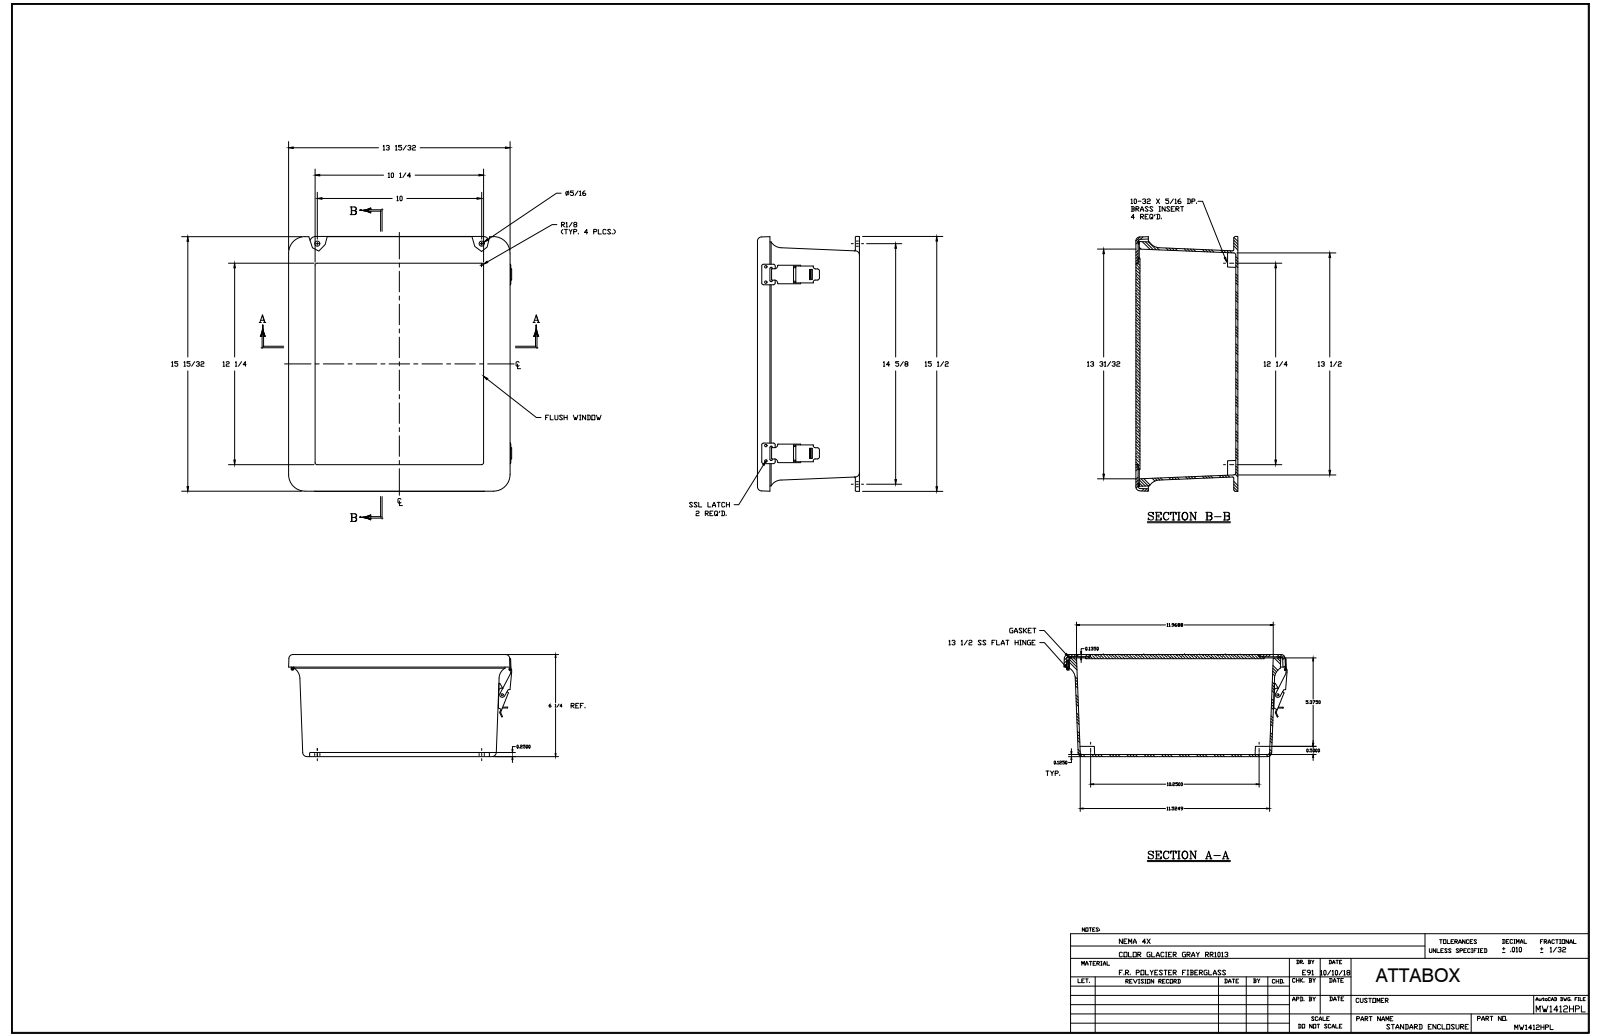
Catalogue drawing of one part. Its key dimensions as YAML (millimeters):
part_name: "MW1412HPL"
step_written_by: "SolidWorks 2018 (AUTOMOTIVE_DESIGN)"
units: millimeters
bodies: {solids: 41, faces: 1073, planar: 472, cylindrical: 452, other: 149}
overall_size: [393.7, 344.6, 157.5]
volume: 2127000
surface_area: 1064000
round_holes:
  - {diameter: 3.6, count: 22}
  - {diameter: 3.3, count: 10}
  - {diameter: 2.6, count: 8}
  - {diameter: 3.9, count: 8}
  - {diameter: 3.3, count: 4}
  - {diameter: 4, count: 4}
  - {diameter: 5.5, count: 4}
  - {diameter: 3.4, count: 2}
  - {diameter: 9.5, count: 2}
  - {diameter: 2.2, count: 1}
  - {diameter: 2.2, count: 1}
  - {diameter: 3.4, count: 1}
round_bosses_or_shafts:
  - {diameter: 3.2, count: 14}
  - {diameter: 6.4, count: 10}
  - {diameter: 6.9, count: 4}
  - {diameter: 3.2, count: 4}
  - {diameter: 7.6, count: 1}
  - {diameter: 4.3, count: 1}
  - {diameter: 3.9, count: 1}
  - {diameter: 3.9, count: 1}
partial_cylinders:
  - {radius: 3.2, count: 24}
  - {radius: 0.4, count: 20}
  - {radius: 0.8, count: 20}
  - {radius: 1.1, count: 16}
  - {radius: 6.4, count: 16}
  - {radius: 0.8, count: 12}
  - {radius: 0.6, count: 8}
  - {radius: 1.5, count: 6}
face_to_face_distances: [3.2, 157.5, 6.4, 151.1, 154.3, 147.9, 3.2, 154, 150.9, 2.9]
hole_center_spacings: [82.6, 165.1, 276.4, 247.7, 276.4, 277.1, 6.4, 76.2]
